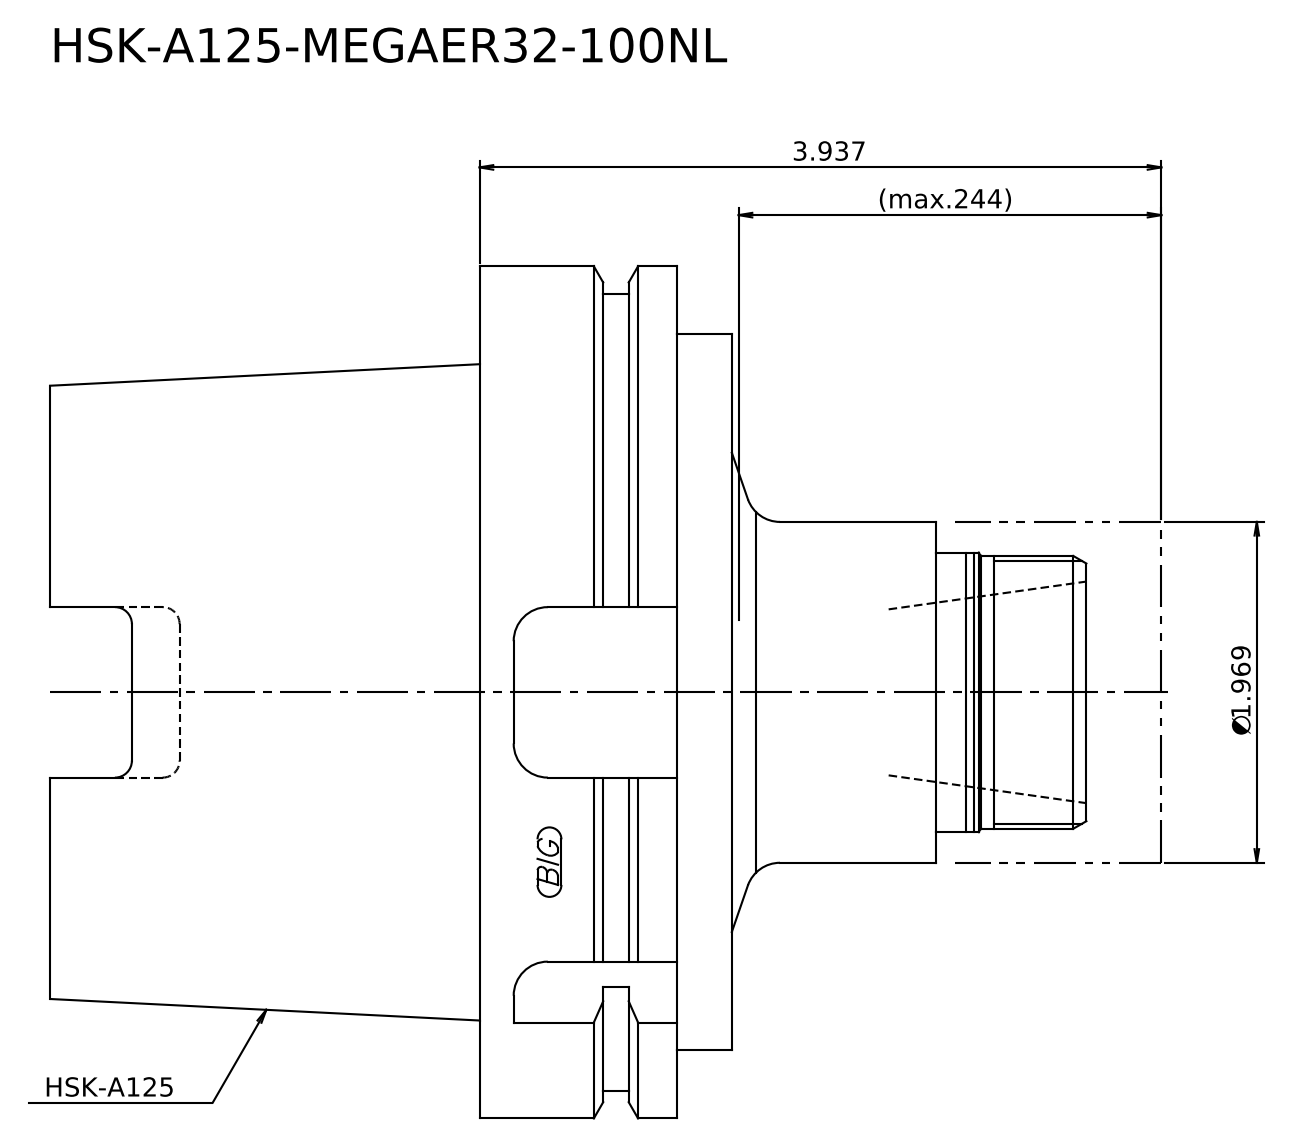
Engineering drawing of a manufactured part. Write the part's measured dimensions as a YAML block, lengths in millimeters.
step_written_by: "Kubotek KeyCreator 2011 V10.0.2 (22737) (automotive_design)"
units: millimeters
bodies: {solids: 2, faces: 24, planar: 10, cylindrical: 8, other: 6}
overall_size: [163, 125, 125]
volume: 999859
surface_area: 73586
round_bosses_or_shafts:
  - {diameter: 125, count: 1}
  - {diameter: 117, count: 1}
  - {diameter: 105, count: 1}
  - {diameter: 50, count: 1}
  - {diameter: 41, count: 1}
  - {diameter: 40, count: 1}
face_to_face_distances: [63, 100, 37, 8, 29, 92, 30.2, 71, 163, 32.8]
